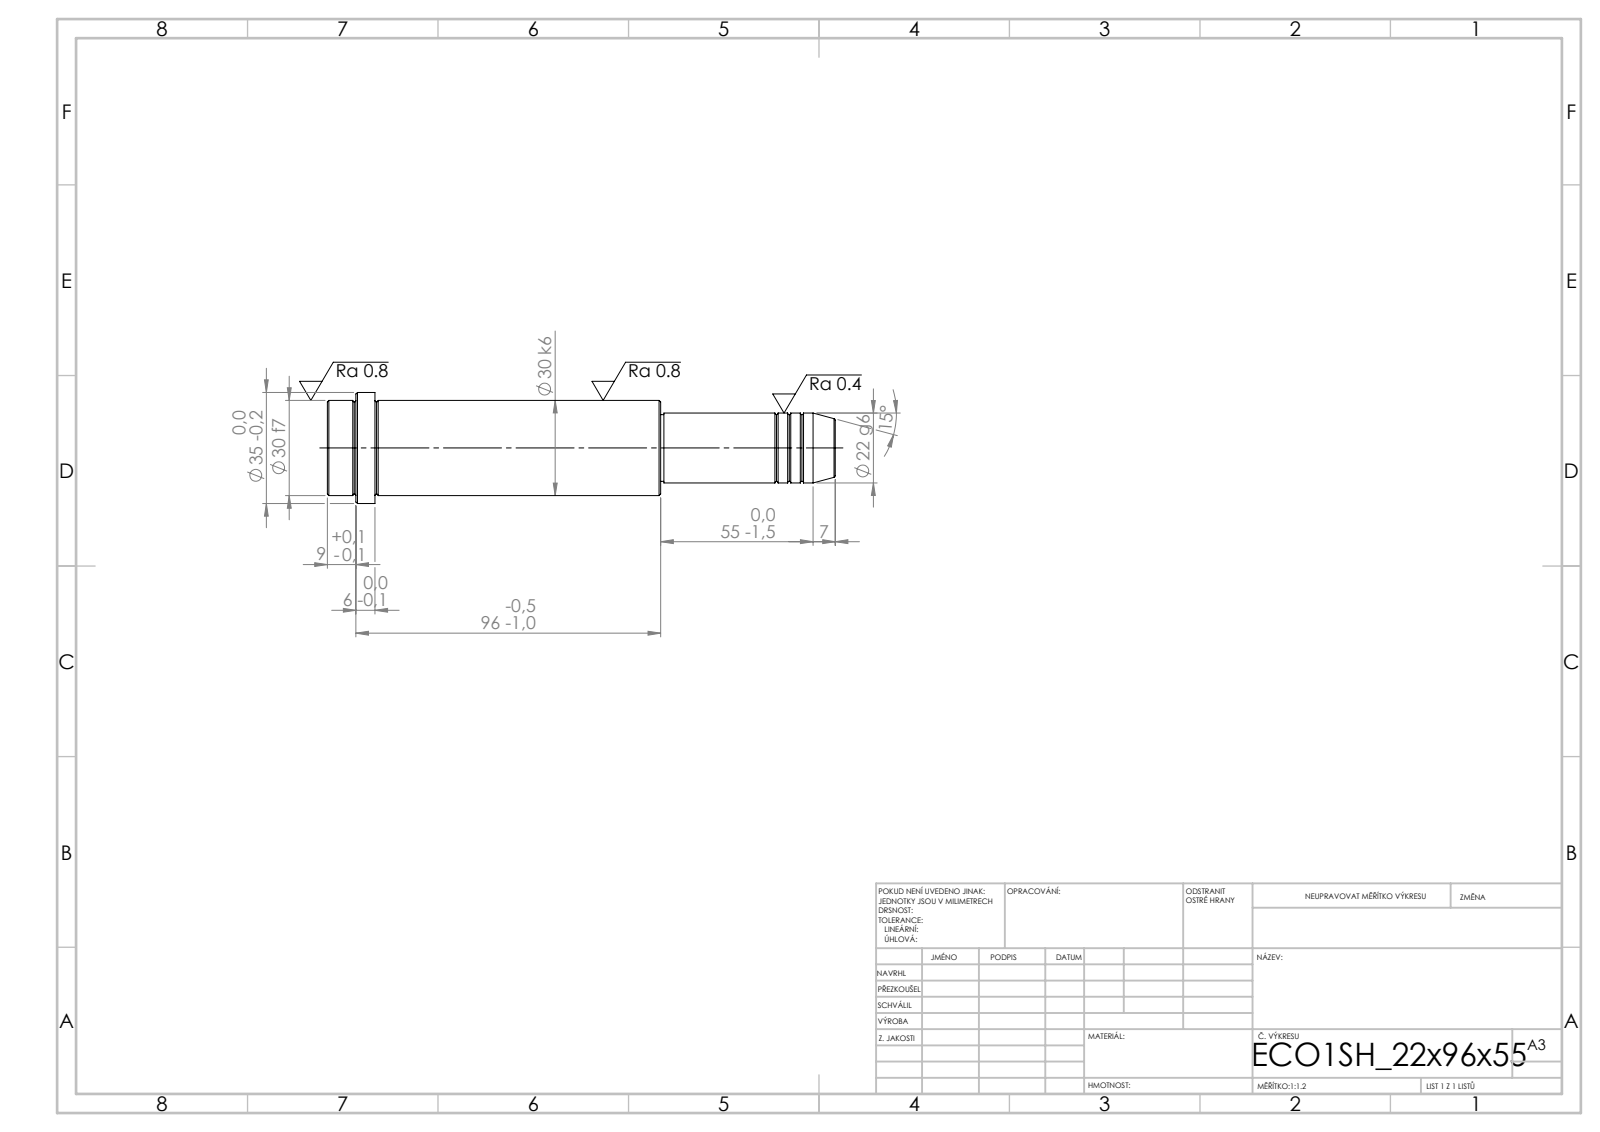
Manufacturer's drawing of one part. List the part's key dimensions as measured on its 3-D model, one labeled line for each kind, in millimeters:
STEP written by: SolidWorks 2019 (CONFIG_CONTROL_DESIGN)
Units: millimetres
Bodies: 1 solid, 52 faces (6 planar, 16 cylindrical, 30 other)
Overall size (bounding box): 160 × 35 × 35
Volume: 96 006 mm³ · Surface area: 15 751 mm²
Round bosses / shafts (diameter × count): ⌀35 ×1, ⌀30 ×1, ⌀22 ×1, ⌀21 ×1
Main face-to-face distances: 105, 90, 15, 55, 145, 160, 151, 96, 6, 9
